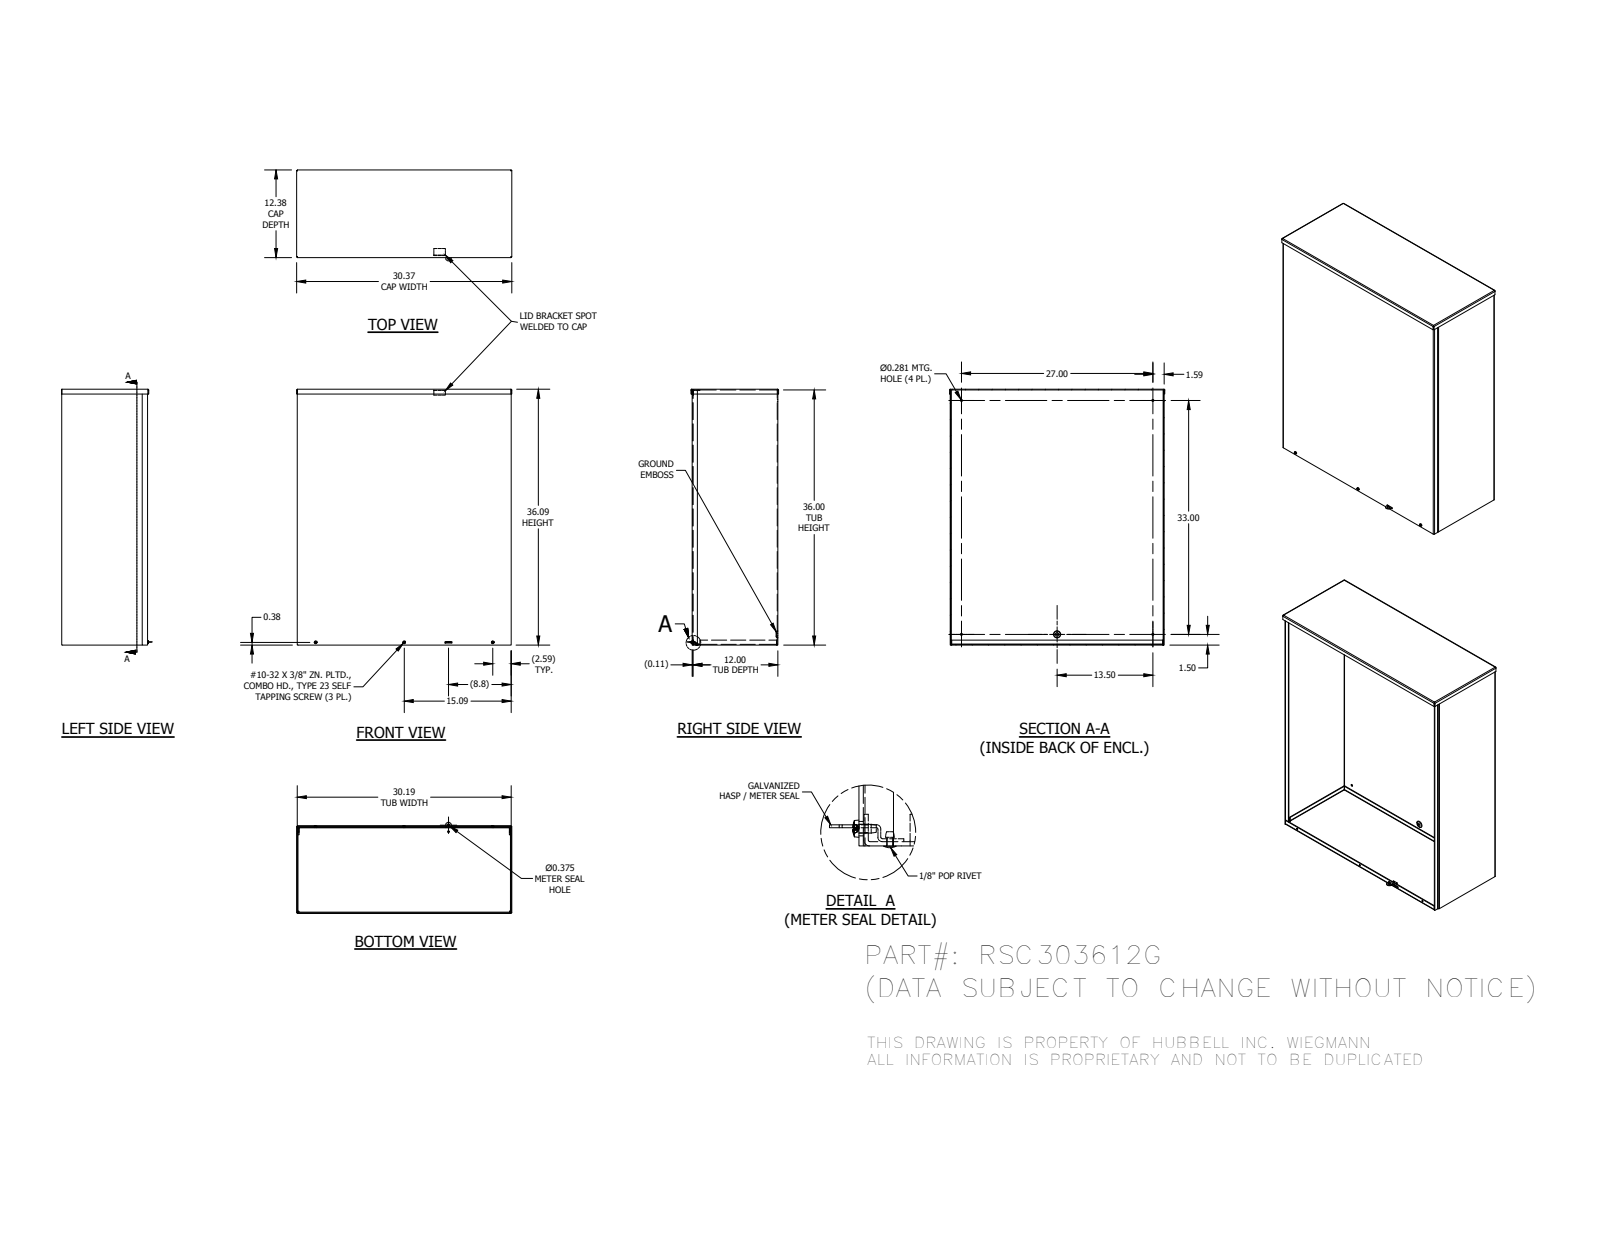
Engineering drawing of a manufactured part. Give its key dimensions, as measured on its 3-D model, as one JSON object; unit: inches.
{"part_name": "RSC303612GBKPA; RSC3012GEWPA; RSC3036GLFA; RSC3012GCPA (+5 more)", "step_written_by": "Autodesk Inventor 2014 (AUTOMOTIVE_DESIGN)", "units": "inches", "bodies": {"solids": 11, "faces": 367, "planar": 226, "cylindrical": 64, "other": 77}, "overall_size": [36.134, 30.375, 12.844], "volume_in3": 366, "surface_area_in2": 7865, "round_holes": [[0.313, 6], [0.171, 4], [0.281, 4], [0.125, 1], [0.136, 1], [0.375, 1]], "round_bosses_or_shafts": [[0.19, 3], [0.262, 1], [0.125, 1]], "partial_cylinders_radius": [[0.031, 19], [0.125, 16], [0.093, 2], [0.105, 1], [0.4, 1]], "face_to_face_distances": [0.094, 12.016, 12.109, 11.922, 30.094, 36, 30.187, 30, 36.094, 35.906], "hole_center_spacings": [12.5, 13.547, 26.024, 25, 1.506, 12.55, 34.14, 36.698]}
